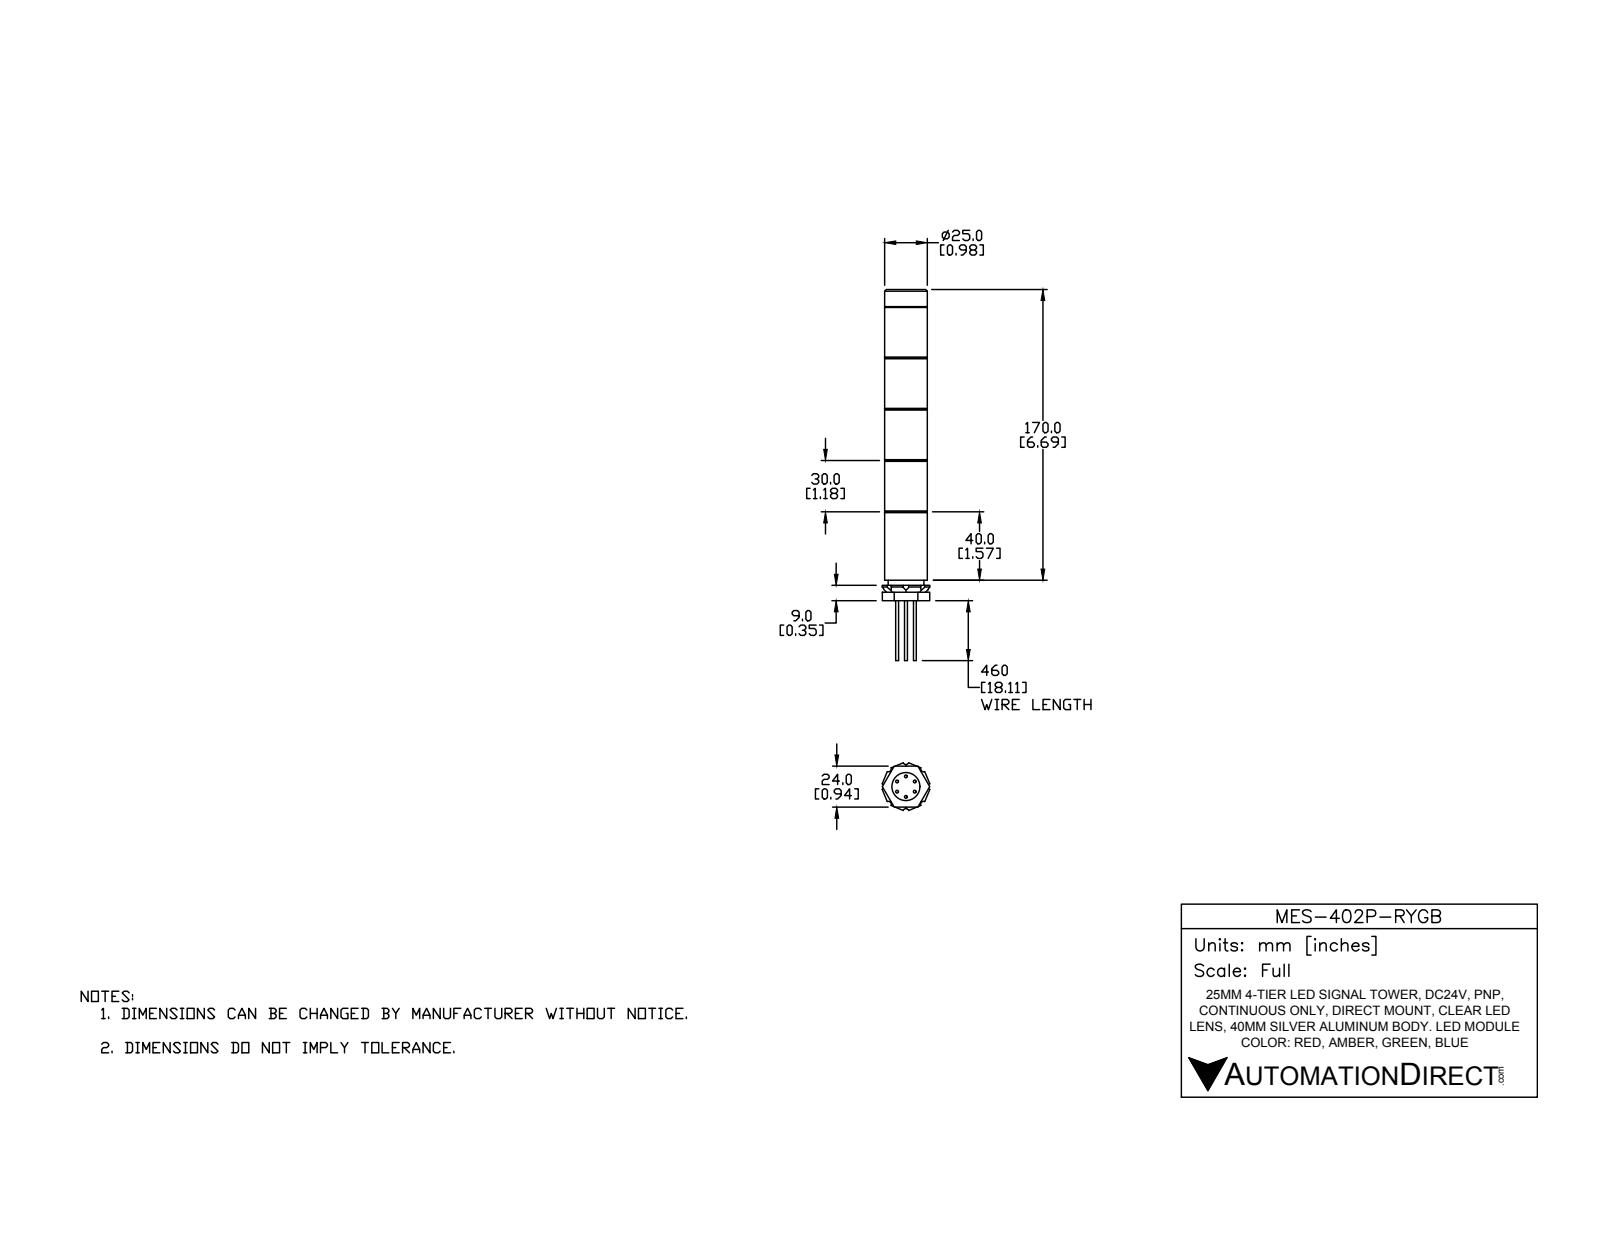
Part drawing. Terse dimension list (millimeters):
name: MES-402P-RYGB
written by: SolidWorks 2016 (AUTOMOTIVE_DESIGN)
unit: mm
bodies: 15 solids, 156 faces (77 planar, 53 cylindrical, 26 other)
size: 217 × 27.89 × 27.89
volume: 77 795 mm³; area: 28 576 mm²
holes: 1× ⌀3.2, 1× ⌀7.7, 1× ⌀16.4, 1× ⌀18, 1× ⌀20.7, 1× ⌀21
bosses: 6× ⌀1.7, 1× ⌀25, 1× ⌀20.9, 1× ⌀16, 1× ⌀5
rounds: 8× R1.75
face distances: 30, 60, 90, 120, 40, 7, 137, 70, 100, 130
